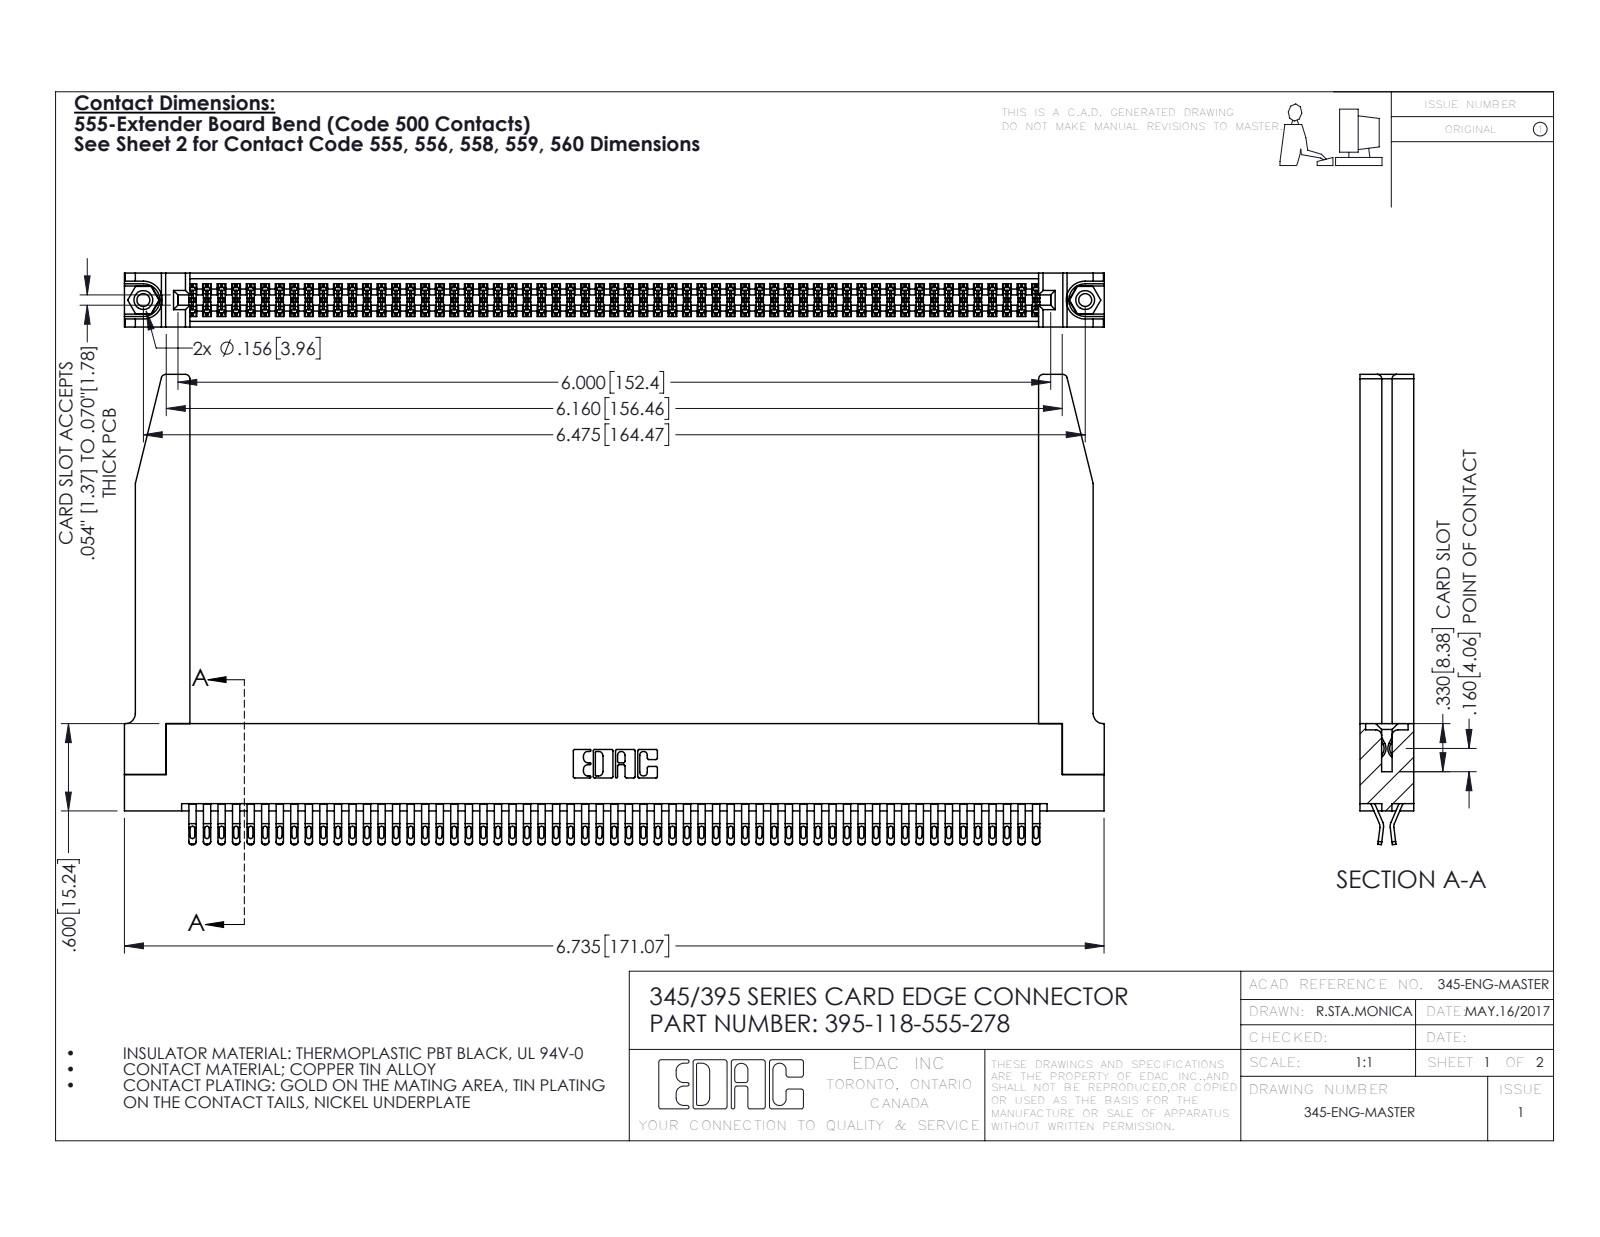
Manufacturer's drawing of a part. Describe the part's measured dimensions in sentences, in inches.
The part is named "345-220-078_345-220-078; 395-118-555-278; 345-250-001_345-250-001-102; 345-292-001_555 Tail (+1 more)". Its 3-D file was written by "SolidWorks 2016 (CONFIG_CONTROL_DESIGN)". It is 123 solids with 6968 faces: 3880 planar, 3036 cylindrical and 52 other. Overall it measures 6.736 by 3.232 by 0.37 inches. Its volume is 1.519 cubic inches and its surface area 52.18 square inches. Round holes: 2 of diameter 0.089, 2 of diameter 0.125, 2 of diameter 0.156, 1 of diameter 0.064. Round bosses or shafts: 2 of diameter 0.155. Partial cylindrical surfaces (rounded edges, fillets, slot ends): 295 of radius 0.016, 236 of radius 0.02, 177 of radius 0.006, 22 of radius 0.01, 8 of radius 0.03, 6 of radius 0.007, 6 of radius 0.031, 3 of radius 0.026. The main face-to-face distances are 0.072, 0.37, 0.298, 0.025, 0.2, 0.098, 0.272, 0.225, 0.175, 0.148. The hole center spacings are 0.27, 6.239, 6.475.
